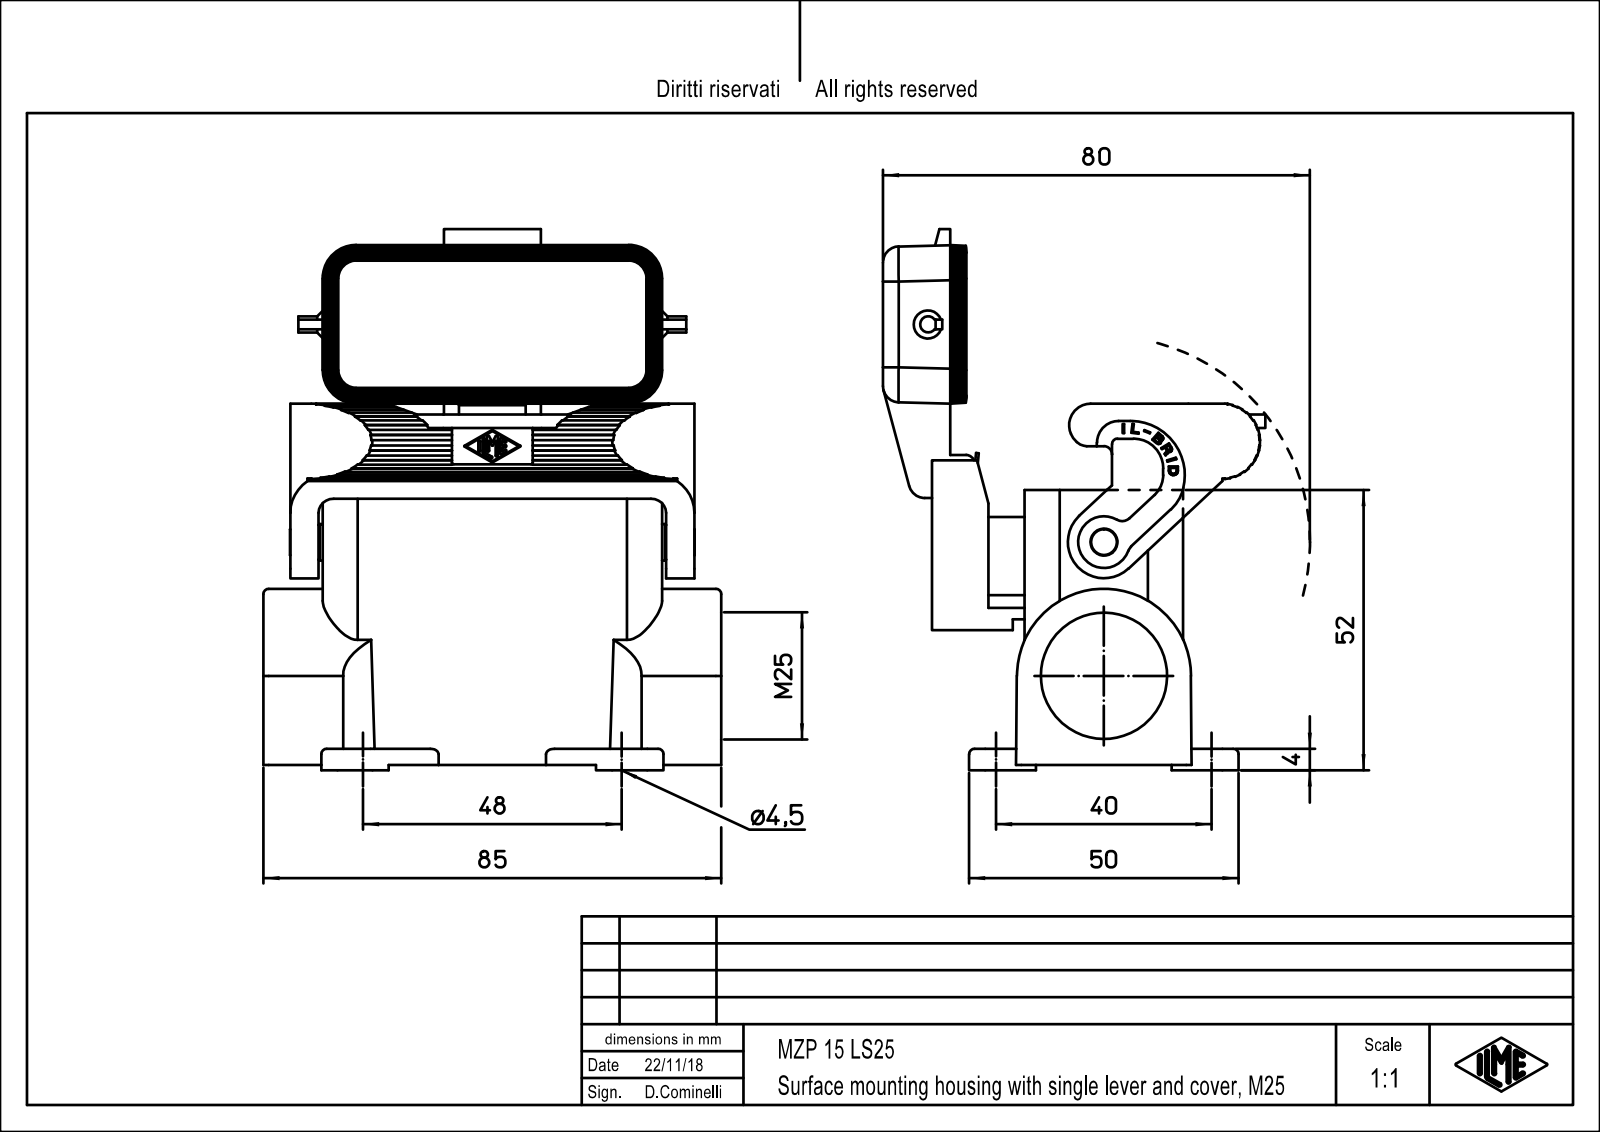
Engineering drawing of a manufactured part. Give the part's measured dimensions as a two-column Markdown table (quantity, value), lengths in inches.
| quantity | value |
| --- | --- |
| part name | MZP_15_LS25 |
| STEP written by | PTC Creo Elements/Direct Modeling 19.0E 27-Jun-2016 (C) Parametric Technology GmbH (AUTOMOTIVE_DESIGN) |
| units | inches |
| bodies | 1 solid, 531 faces (304 planar, 193 cylindrical, 34 other) |
| overall size | 3.953 × 3.346 × 2.795 |
| volume | 4.706 in³ |
| surface area | 73.85 in² |
| round holes (diameter × count) | 0.118 × 4, 0.177 × 4, 0.197 × 1, 0.827 × 1, 0.929 × 1 |
| round bosses / shafts (diameter × count) | 0.276 × 1, 0.268 × 1, 0.189 × 1, 0.118 × 1 |
| partial cylindrical surfaces (radius × count) | 0.008 × 15, 0.118 × 14, 0.039 × 13, 0.256 × 8, 0.138 × 4, 0.138 × 4, 0.236 × 4, 0.004 × 3 |
| main face-to-face distances | 0.102, 1.055, 0.953, 1.157, 2.264, 0.079, 0.118, 1.059, 2.114, 2.012 |
| hole center spacings | 0.473, 1.103, 1.977, 2.213, 0.63, 1.575, 1.89, 1.949 |
